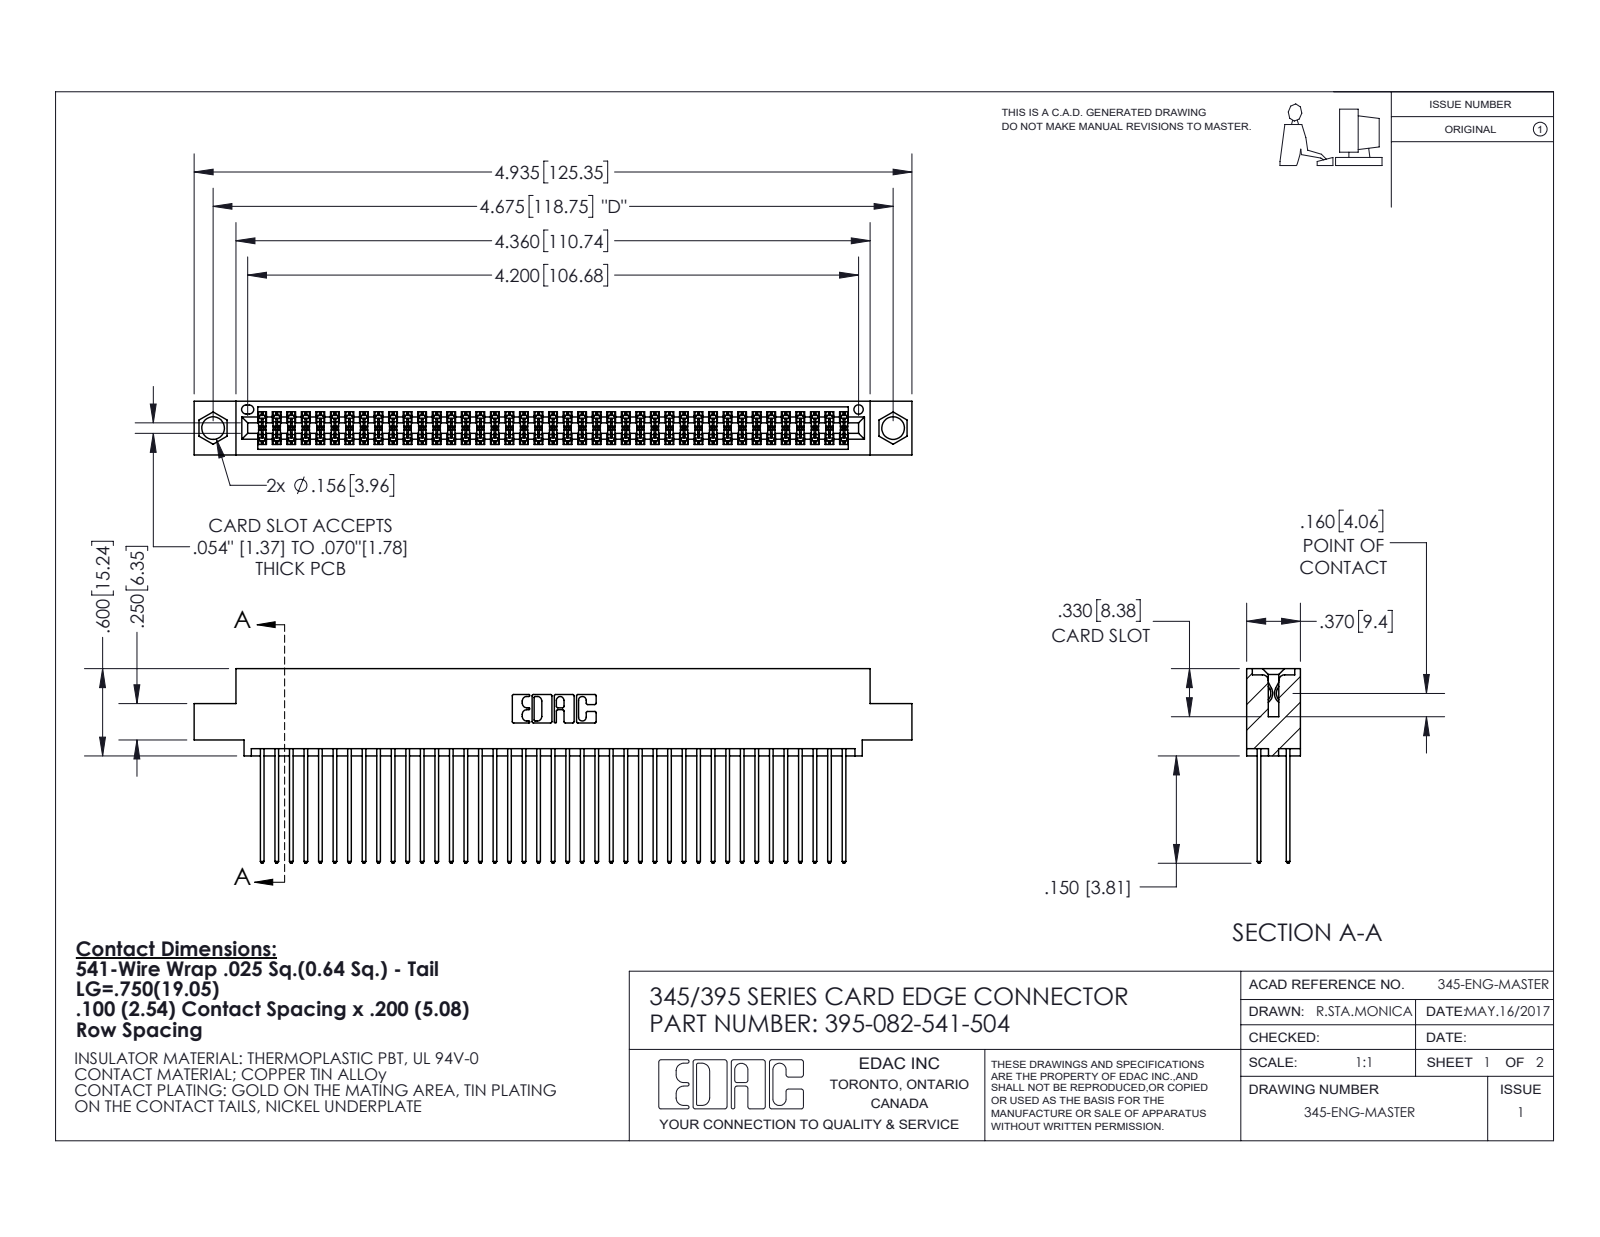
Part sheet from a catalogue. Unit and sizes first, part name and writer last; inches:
Units: inches
Overall size (bounding box): 4.935 × 1.337 × 0.37
Round holes (diameter × count): ⌀0.156 ×2, ⌀0.064 ×1
Partial cylindrical surfaces — rounded edges, fillets, slot ends (radius × count): R0.006 ×123, R0.01 ×82, R0.01 ×22, R0.007 ×6, R0.031 ×6, R0.026 ×3, R0.014 ×2, R0.019 ×2
Main face-to-face distances: 0.298, 0.072, 0.2, 0.098, 0.272, 0.025, 0.225, 0.37, 0.175, 0.149
Hole centre spacings: 0.27, 4.439, 4.675
Volume: 0.76 in³ · Surface area: 31.86 in²
Bodies: 83 solids, 4244 faces (2804 planar, 1440 cylindrical, 0 other)
Part name (STEP PRODUCT): 345-292-001_345-293-141; 395-082-541-504; 345 Part_0.110 Offset - 0.156 Dia-TI
STEP written by: SolidWorks 2020 (CONFIG_CONTROL_DESIGN)
